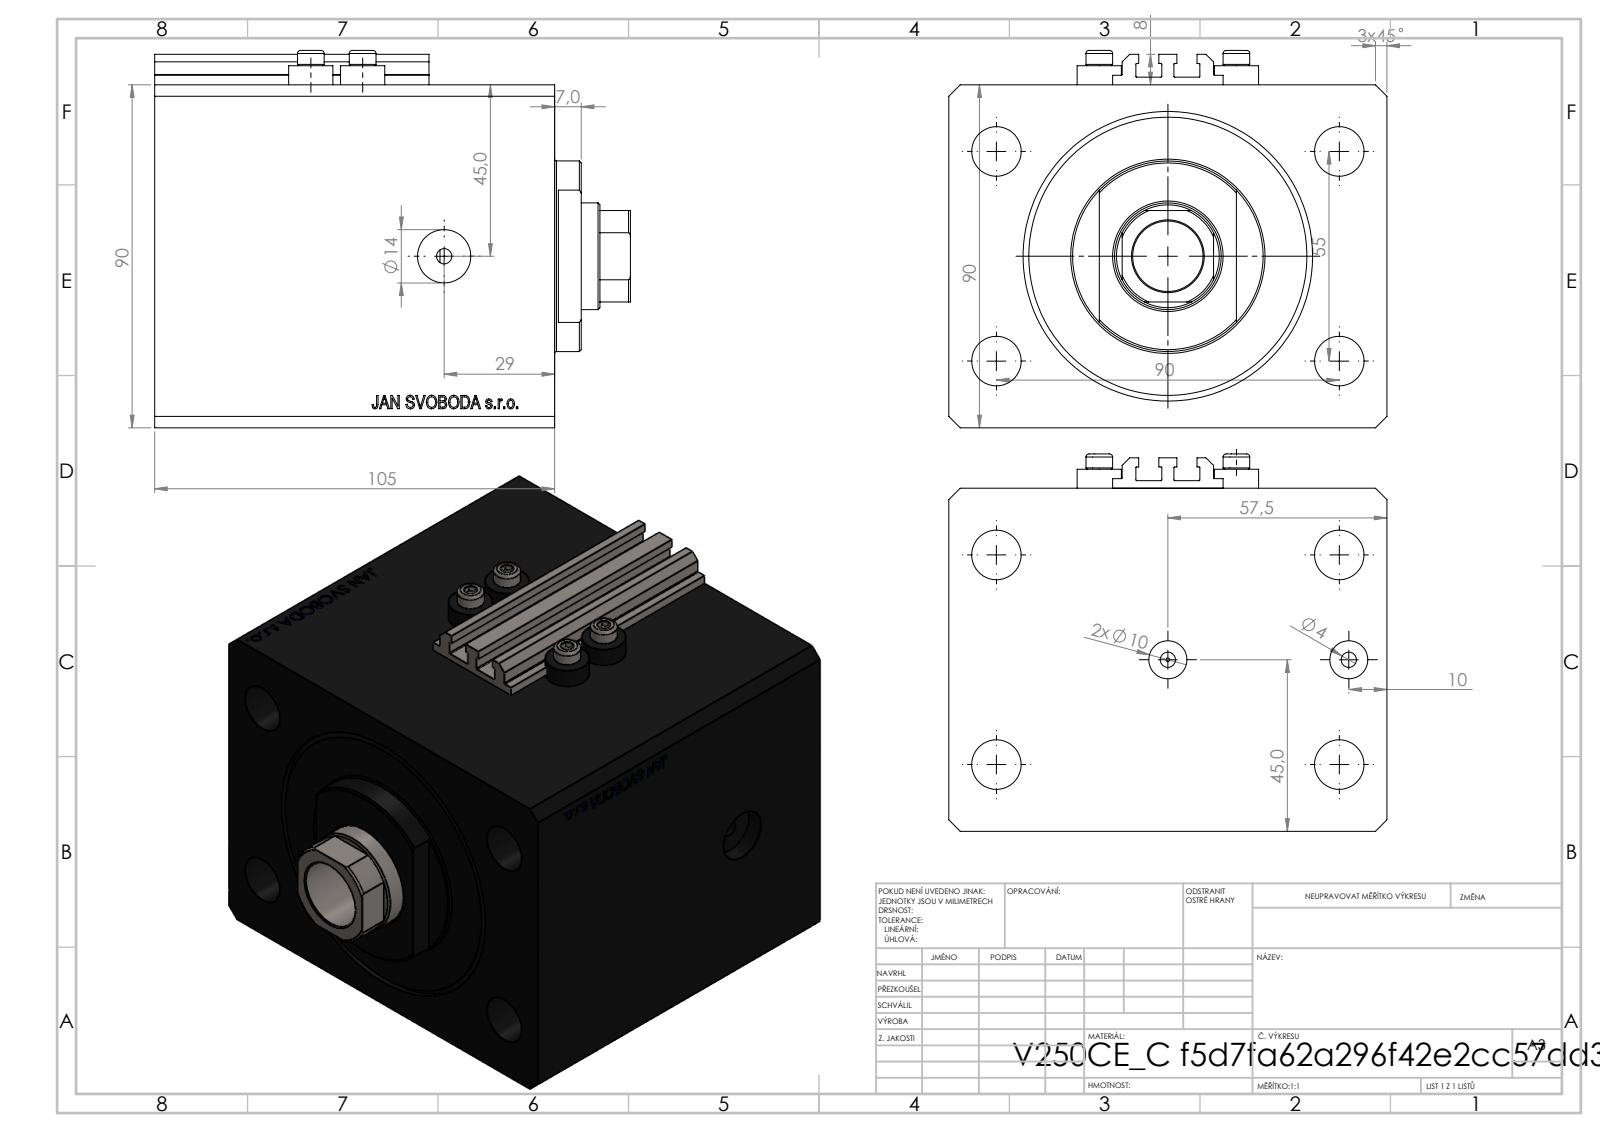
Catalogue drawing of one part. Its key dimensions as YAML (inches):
part_name: "V250CE_C_Body; ALLEN BOLT V250CE; V250CE_C_VCP; V250CE_VC_C"
step_written_by: "SolidWorks 2019 (CONFIG_CONTROL_DESIGN)"
units: inches
bodies: {solids: 8, faces: 1038, planar: 504, cylindrical: 88, other: 446}
overall_size: [4.917, 4.528, 3.898]
volume: 60.8
surface_area: 233.6
round_holes:
  - {diameter: 0.157, count: 8}
  - {diameter: 0.512, count: 4}
  - {diameter: 0.394, count: 2}
  - {diameter: 0.551, count: 2}
  - {diameter: 0.049, count: 1}
  - {diameter: 0.728, count: 1}
  - {diameter: 1.102, count: 1}
  - {diameter: 2.48, count: 1}
  - {diameter: 2.992, count: 1}
round_bosses_or_shafts:
  - {diameter: 0.457, count: 4}
  - {diameter: 0.276, count: 4}
  - {diameter: 1.969, count: 1}
partial_cylinders:
  - {radius: 0.008, count: 10}
  - {radius: 0.531, count: 1}
face_to_face_distances: [3.543, 4.528, 4.134, 3.429, 0.705, 2.244, 2.949, 1.185, 2.161, 1.457]
hole_center_spacings: [2.076, 0.535, 1.087, 1.417, 1.515, 2.165, 3.543, 3.799]
